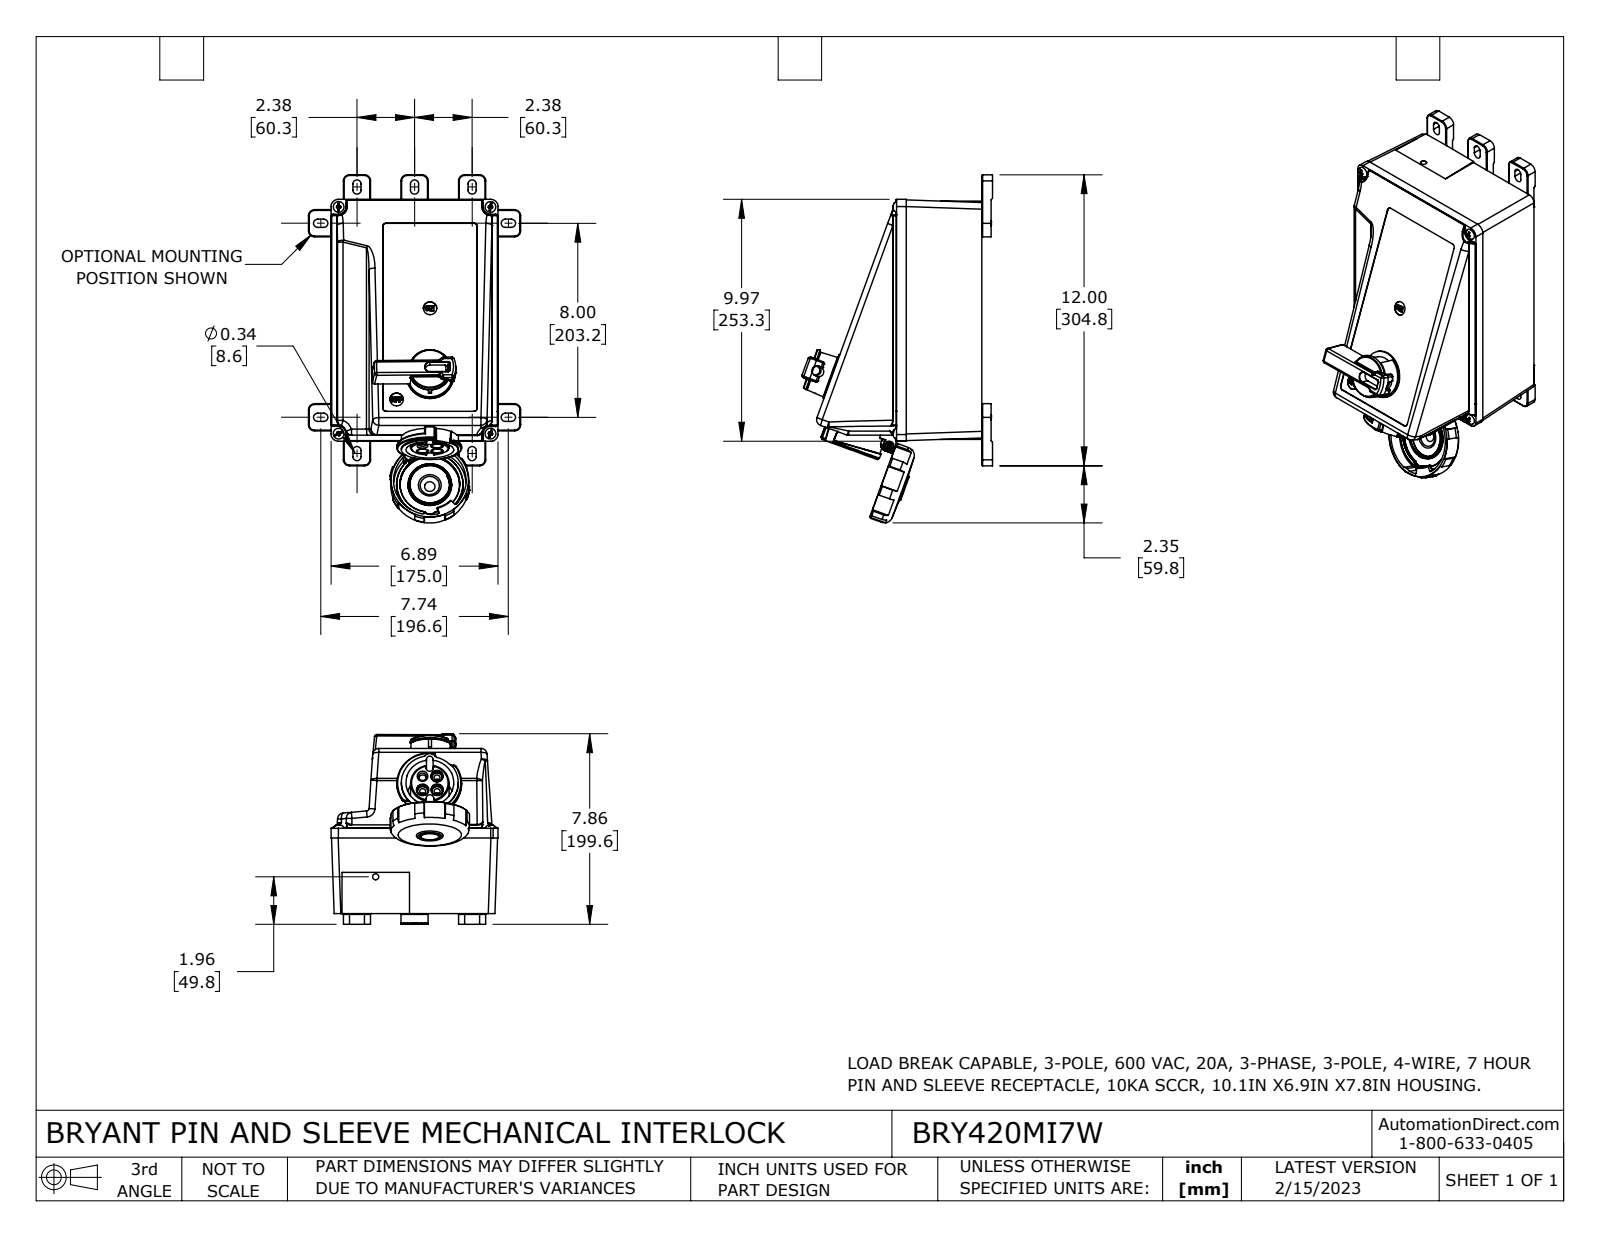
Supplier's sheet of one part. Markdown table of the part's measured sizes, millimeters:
| quantity | value |
| --- | --- |
| part name | BRY420MI7W |
| STEP written by | SolidWorks 2021 (CONFIG_CONTROL_DESIGN) |
| units | millimeters |
| bodies | 10 solids, 2065 faces (740 planar, 671 cylindrical, 654 other) |
| overall size | 364.6 × 199.6 × 175 |
| volume | 5 488 000 mm³ |
| surface area | 300 000 mm² |
| round holes (diameter × count) | 7.1 × 5, 2 × 4, 6.3 × 3, 4 × 2, 14.2 × 2, 2.6 × 1, 3.5 × 1, 4 × 1, 6.4 × 1, 6.9 × 1, 8.3 × 1, 16.8 × 1 |
| round bosses / shafts (diameter × count) | 6.7 × 2, 3.1 × 2, 69.6 × 1, 59.7 × 1, 48.8 × 1, 45.6 × 1, 40.3 × 1, 31.6 × 1 |
| partial cylindrical surfaces (radius × count) | 0.4 × 124, 0.8 × 54, 2 × 30, 6.4 × 24, 2.3 × 17, 0.3 × 16, 1.9 × 12, 4.3 × 10 |
| main face-to-face distances | 3, 245.2, 120.7, 249.7, 4.4, 105.9, 105.6, 3.8, 9.7, 0.9 |
| hole center spacings | 17.8, 10.7, 15.2, 12.1, 25.8, 10.7, 10.8, 17.8 |
